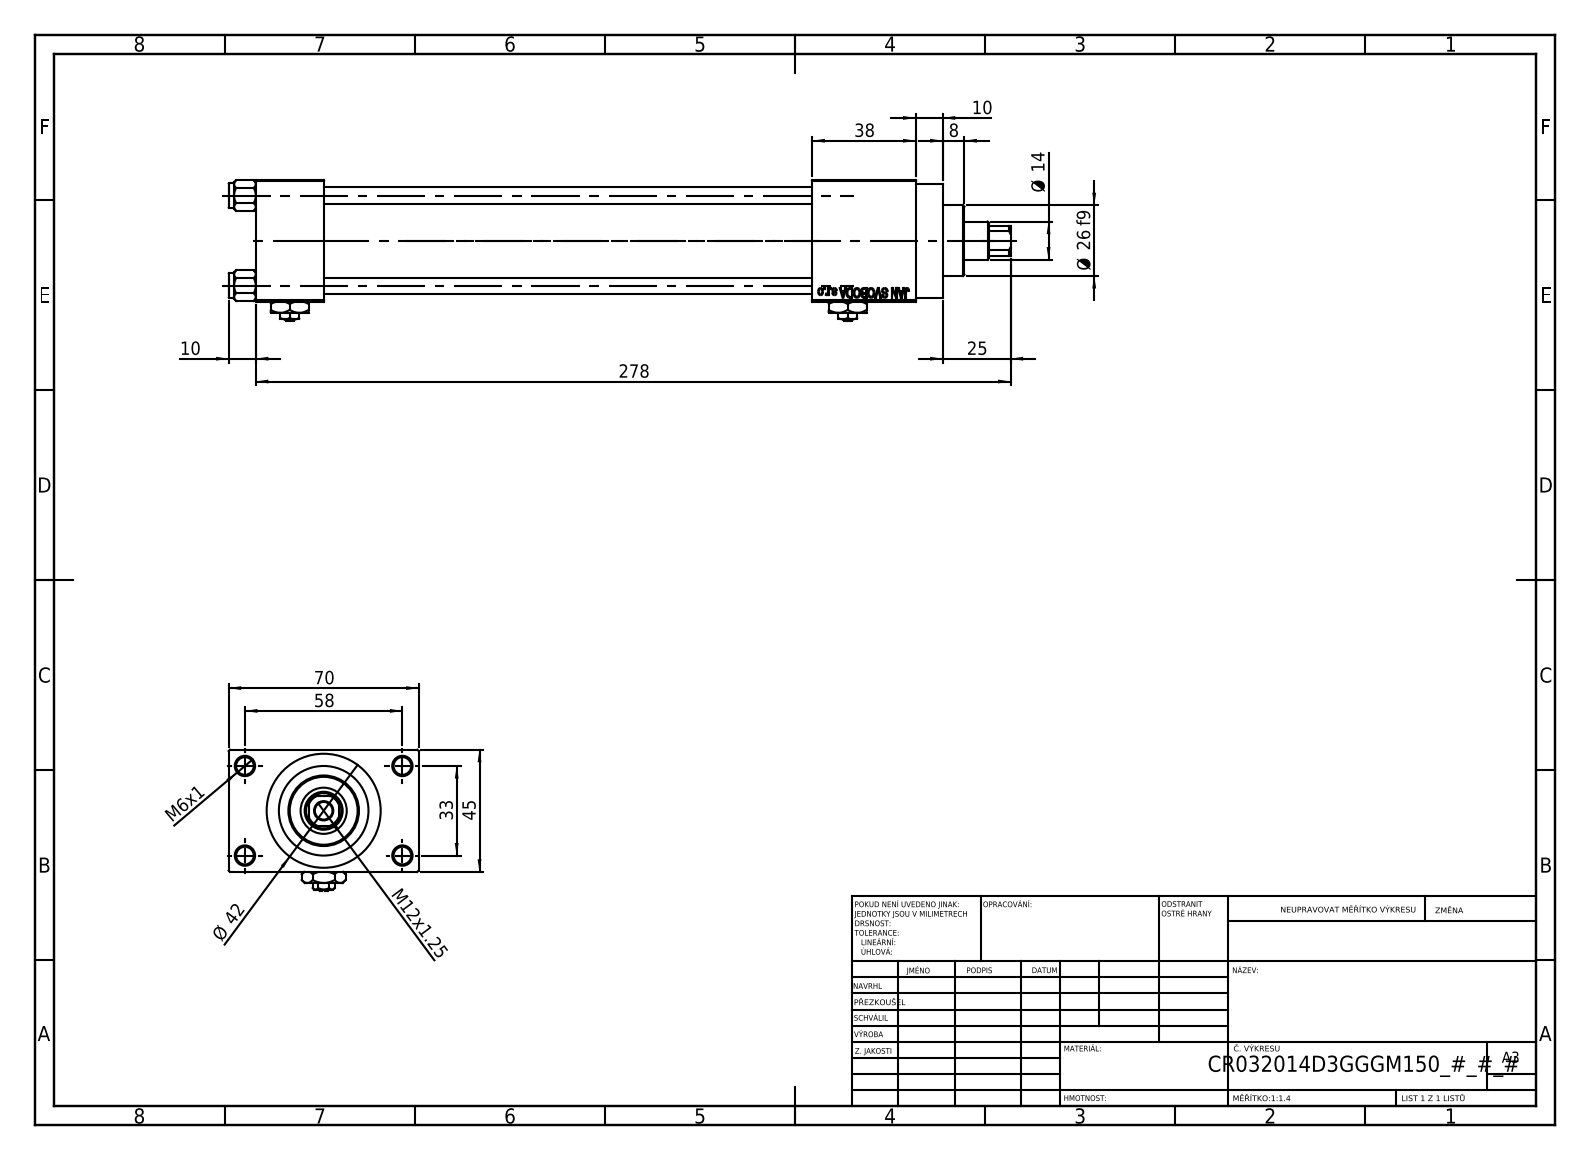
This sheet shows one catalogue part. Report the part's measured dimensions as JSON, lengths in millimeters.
{"part_name": "V215CR_VCP_D; Zatka_pro_OIL_PORT; V215CR_D_Body; V215CR_D_TYCINKA (+2 more)", "step_written_by": "SolidWorks 2019 (CONFIG_CONTROL_DESIGN)", "units": "millimeters", "bodies": {"solids": 13, "faces": 1202, "planar": 542, "cylindrical": 100, "other": 560}, "overall_size": [288, 70, 52], "volume_mm3": 308295, "surface_area_mm2": 120725, "round_holes": [[6.5, 5], [6, 4], [7, 2], [13.16, 2], [20, 2], [14, 1], [17, 1], [24, 1], [32, 1], [33, 1]], "round_bosses_or_shafts": [[9, 4], [42, 1], [38, 1], [26, 1]], "partial_cylinders_radius": [[6.5, 1]], "face_to_face_distances": [45, 25, 12.5, 57.5, 180, 205, 218, 70, 38, 243], "hole_center_spacings": [12.4, 23.48, 33.2, 33.37, 35.35, 45.6, 56.35, 33]}
